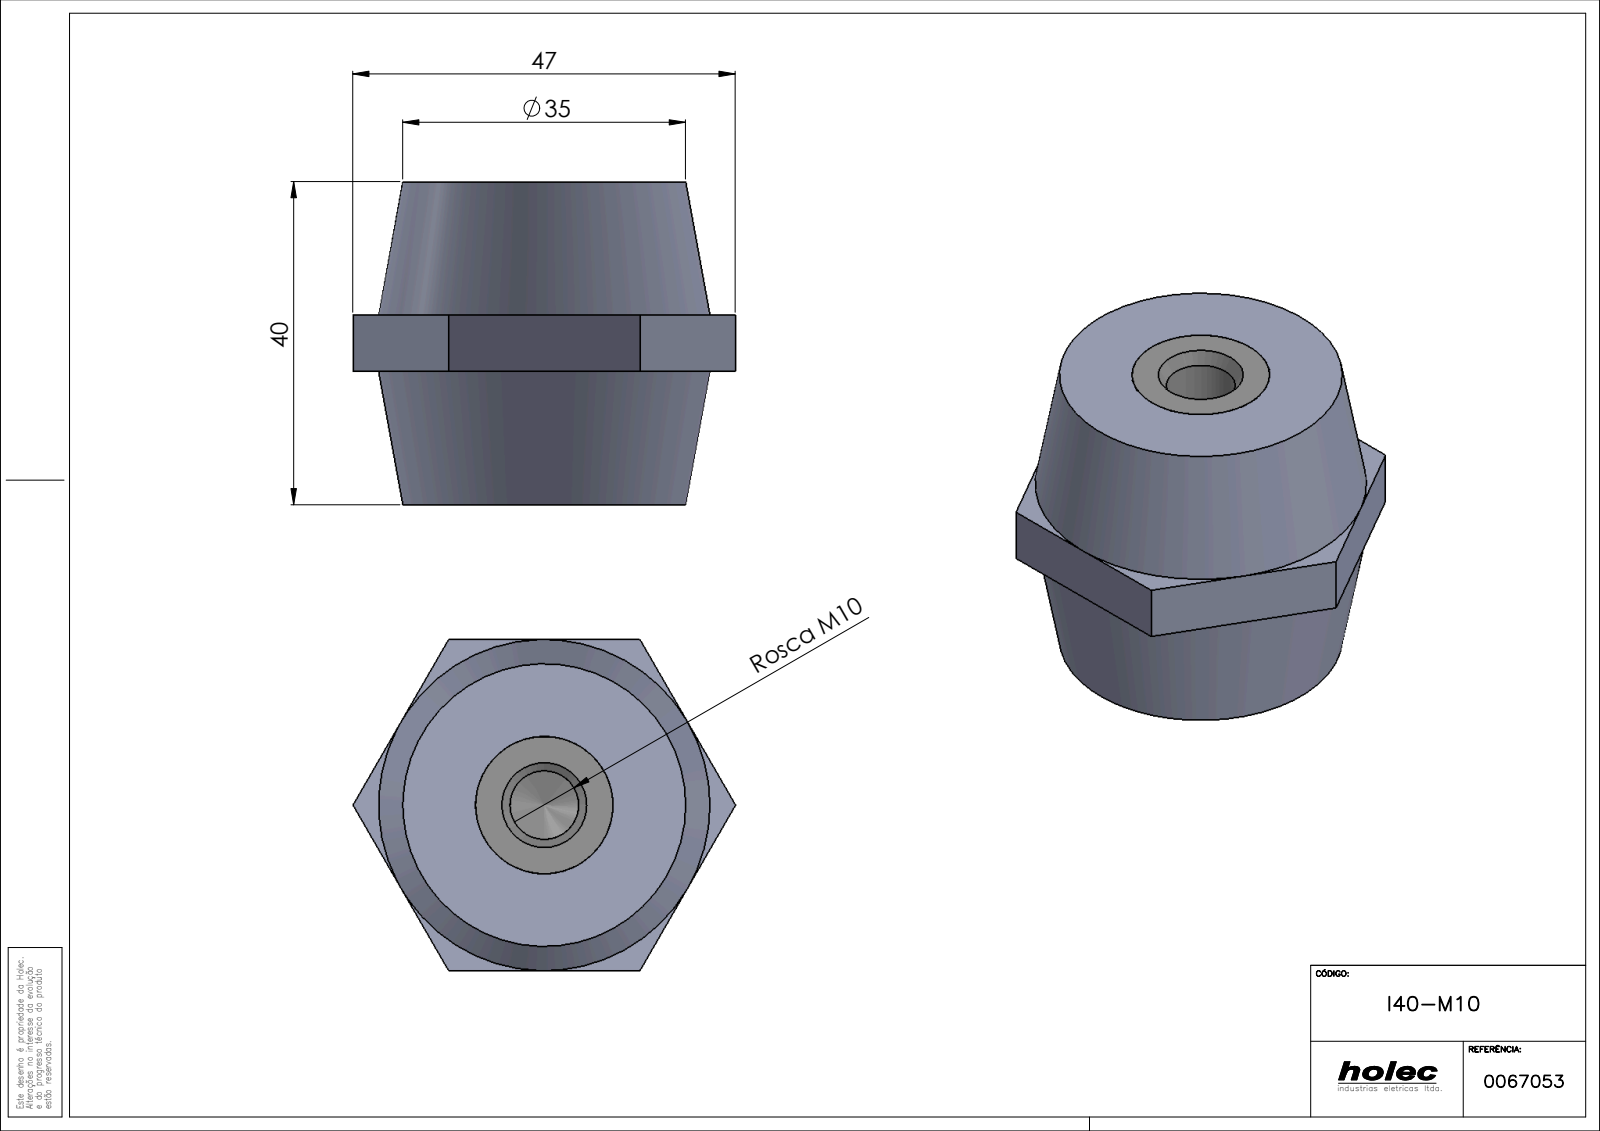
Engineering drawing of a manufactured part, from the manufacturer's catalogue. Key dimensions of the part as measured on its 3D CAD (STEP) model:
Part name (STEP PRODUCT): PB1_0104(PB1_0104_10); PB1_0002; I40-M10
STEP written by: SolidWorks 2017 (AUTOMOTIVE_DESIGN)
Units: millimetres
Bodies: 3 solids, 162 faces (82 planar, 12 cylindrical, 68 other)
Overall size (bounding box): 47.34 × 41 × 40
Volume: 45 974 mm³ · Surface area: 13 240 mm²
Round holes (diameter × count): ⌀8.5 ×1, ⌀14 ×1
Main face-to-face distances: 17, 40, 23.01, 23, 5, 12, 7, 41, 16.99, 6.01
